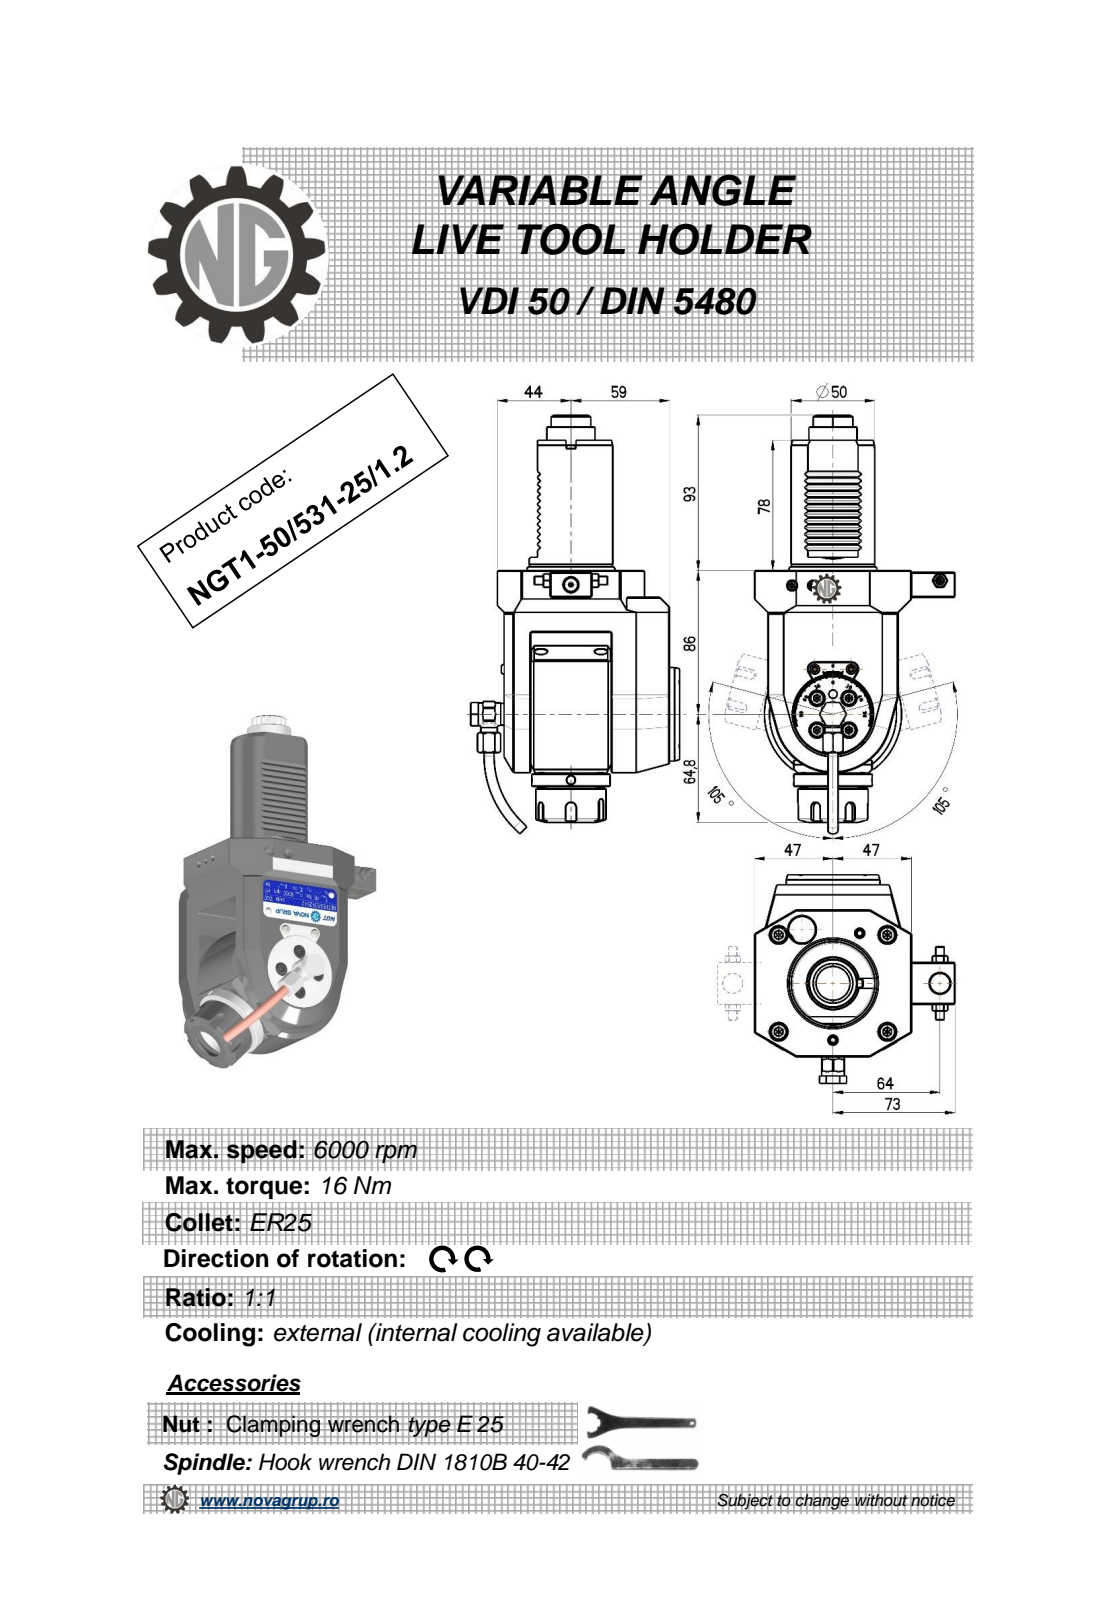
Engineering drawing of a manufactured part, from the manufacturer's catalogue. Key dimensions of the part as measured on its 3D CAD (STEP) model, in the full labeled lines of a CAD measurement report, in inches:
Part name (STEP PRODUCT): NGT1_50_531_25_1_2
STEP written by: PRO/ENGINEER BY PARAMETRIC TECHNOLOGY CORPORATION, 2010280 (CONFIG_CONTROL_DESIGN)
Units: inches
Bodies: 1 solid, 700 faces (265 planar, 209 cylindrical, 226 other)
Overall size (bounding box): 9.869 × 4.917 × 4.724
Volume: 62.55 in³ · Surface area: 141.6 in²
Round holes (diameter × count): ⌀0.157 ×3, ⌀0.197 ×2, ⌀0.118 ×1, ⌀0.165 ×1, ⌀0.244 ×1, ⌀0.354 ×1, ⌀0.374 ×1, ⌀0.394 ×1, ⌀0.433 ×1, ⌀0.472 ×1, ⌀0.799 ×1
Round bosses / shafts (diameter × count): ⌀0.236 ×2, ⌀0.224 ×2, ⌀3.228 ×1, ⌀2.205 ×1, ⌀1.969 ×1, ⌀1.85 ×1, ⌀1.654 ×1, ⌀1.378 ×1
Partial cylindrical surfaces — rounded edges, fillets, slot ends (radius × count): R0.12 ×36, R0.01 ×12, R0.012 ×12, R0.006 ×6, R0.118 ×5, R0.02 ×4, R0.039 ×2, R0.394 ×2
Main face-to-face distances: 1.457, 3.898, 0.63, 3.071, 0.315, 0.787, 0.236, 2.52, 4.134, 0.827
Hole centre spacings: 0.016, 1.553, 1.929, 1.945, 2.52, 3.173, 3.183, 4.033
